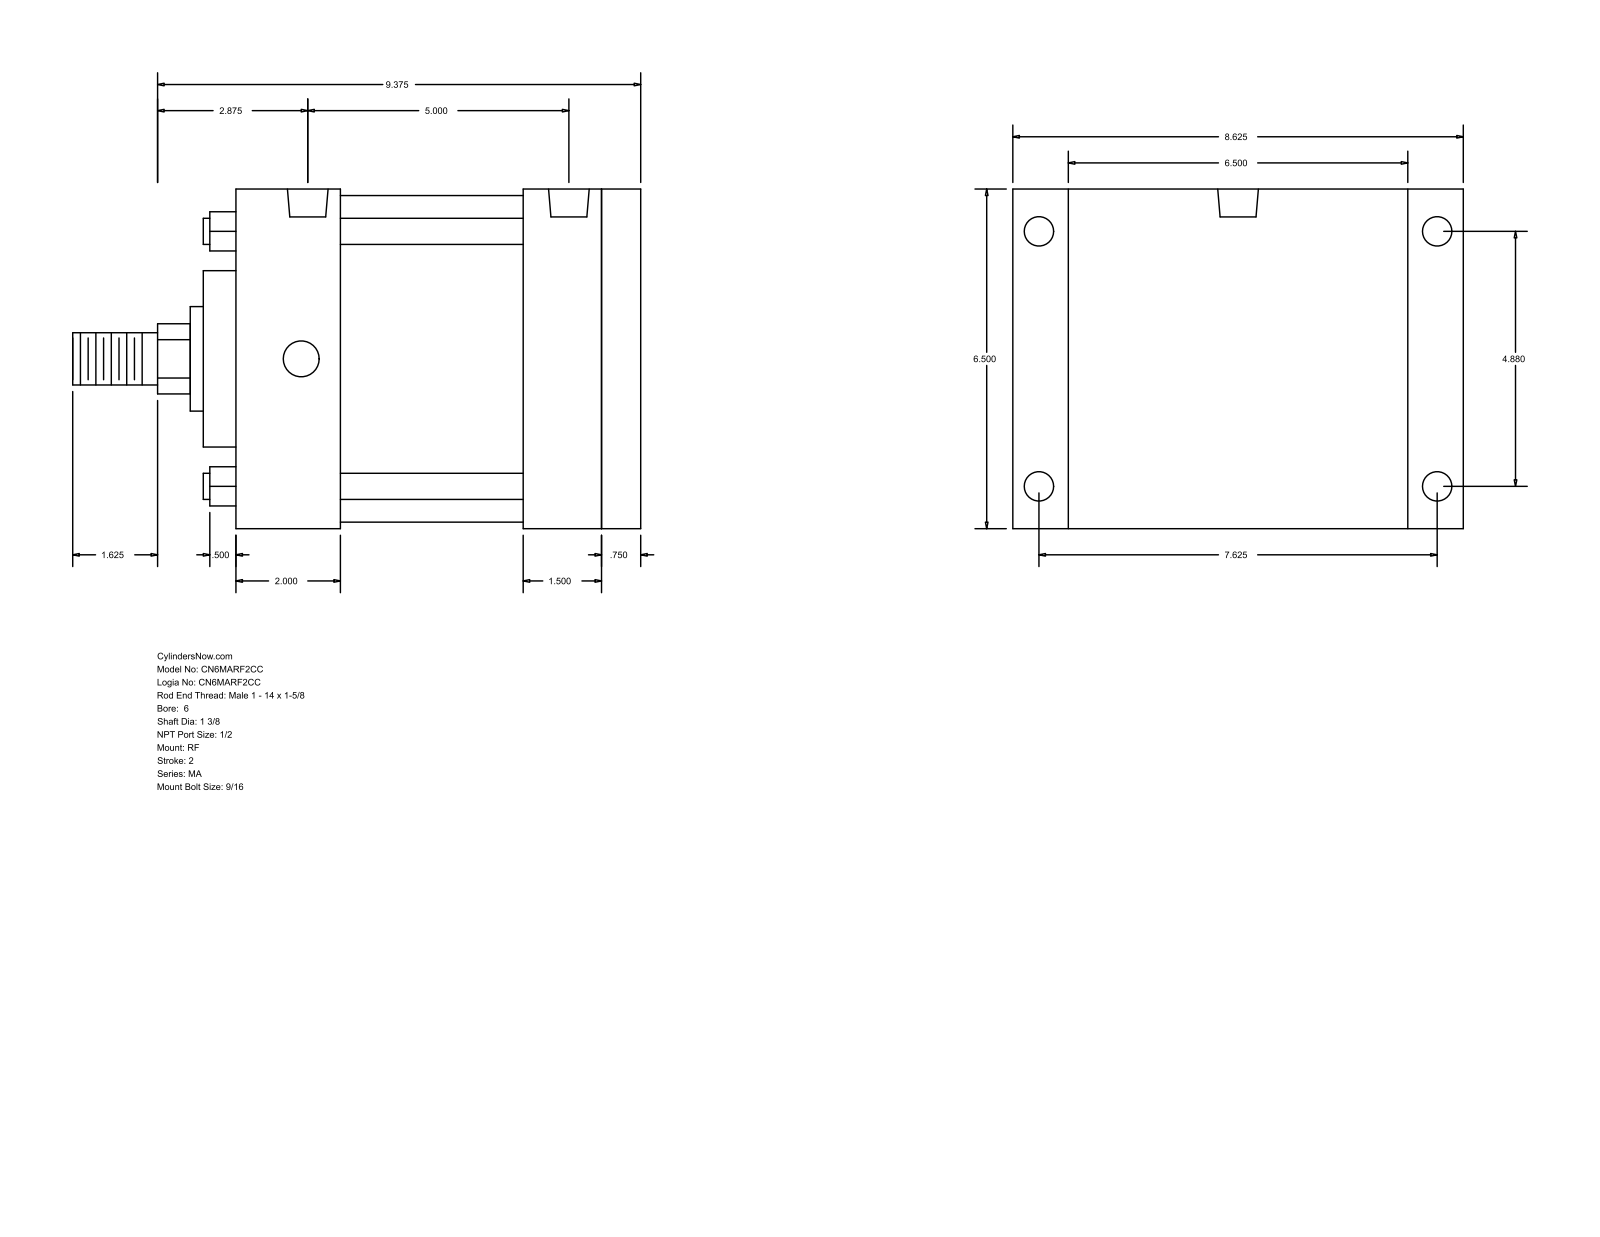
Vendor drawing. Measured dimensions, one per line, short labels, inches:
name: MA_RF__0600_1.375
written by: GSSL Pune (CONFIG_CONTROL_DESIGN)
unit: in
bodies: 0 solids, 94 faces (65 planar, 29 cylindrical, 0 other)
size: 11 × 8.625 × 6.5
holes: 4× ⌀0.563, 4× ⌀0.687, 2× ⌀0.778
bosses: 4× ⌀0.5, 1× ⌀6.25, 1× ⌀3.375, 1× ⌀2, 1× ⌀1.375, 1× ⌀1
rounds: 1× R0.672
face distances: 6.5, 7.875, 0.75, 7.125, 5.125, 2.25, 1.5, 2, 5.875, 5.625
hole spacings: 4.88, 5.125, 7.625, 9.053, 0.125, 5
